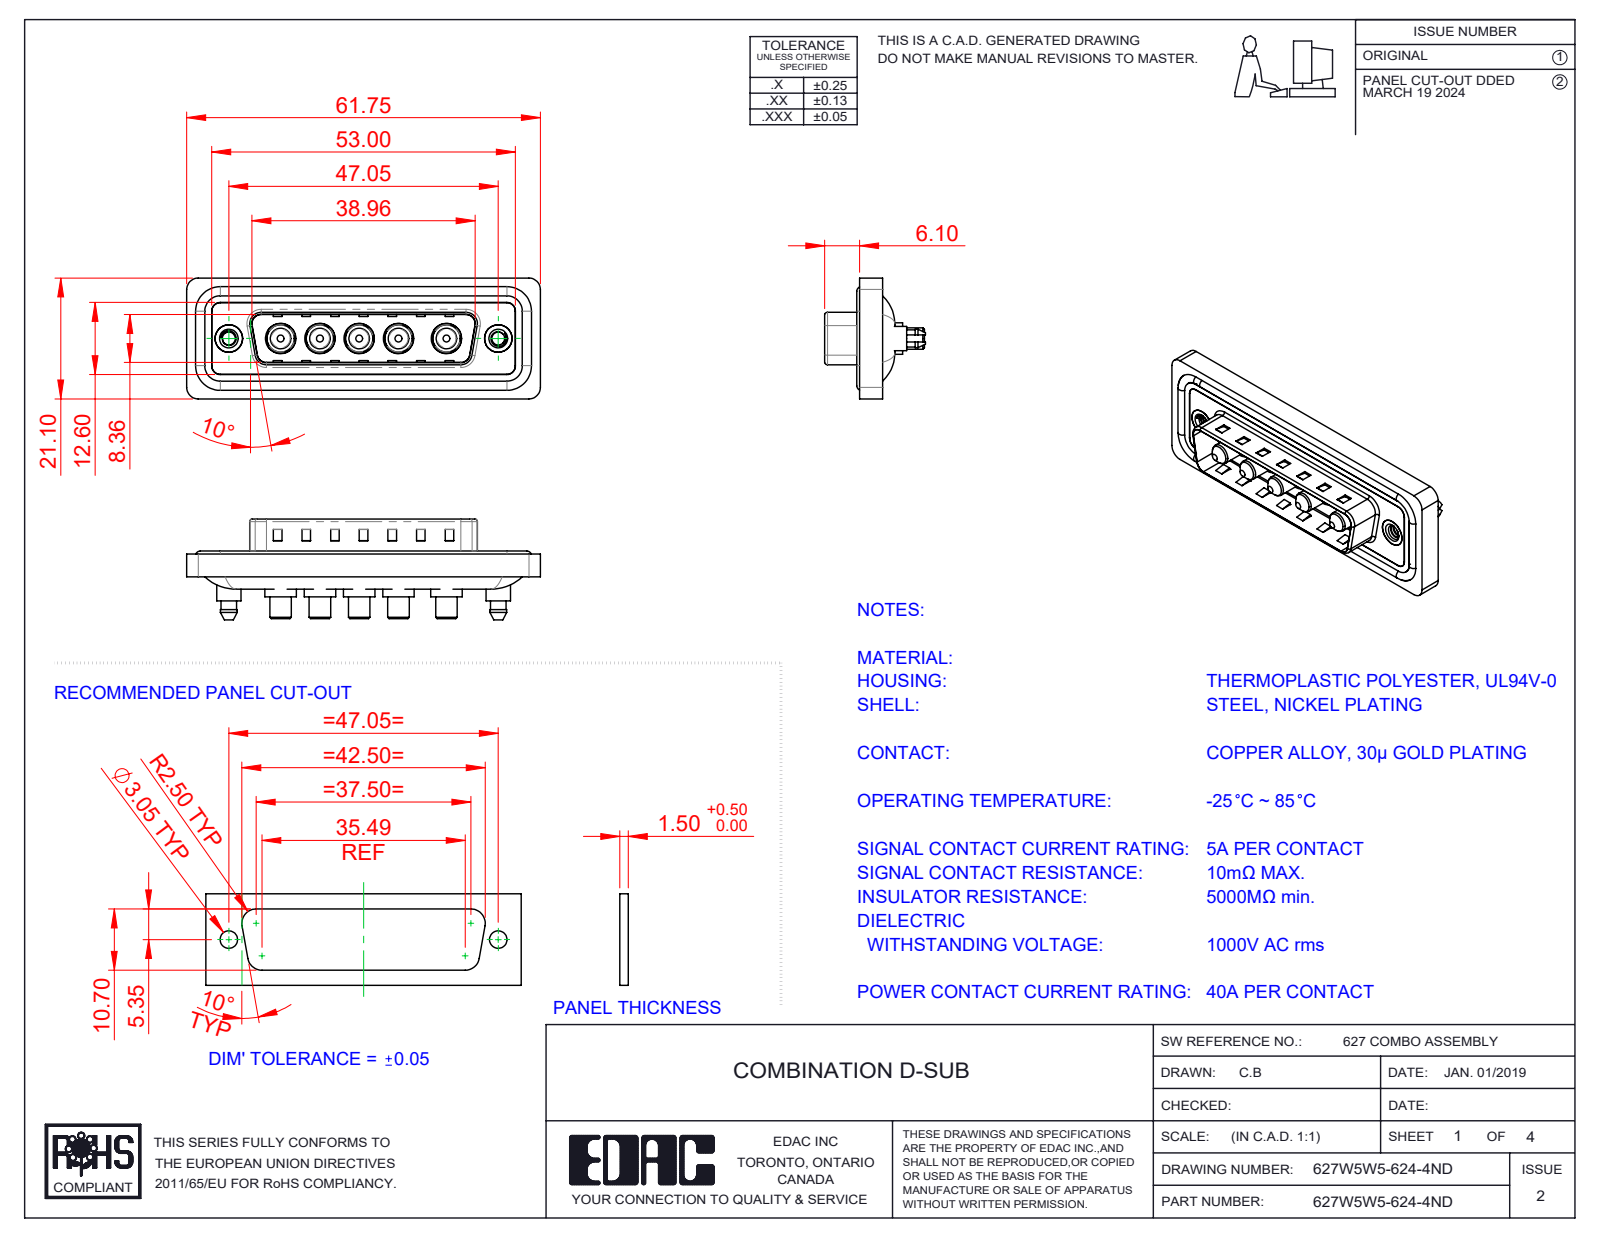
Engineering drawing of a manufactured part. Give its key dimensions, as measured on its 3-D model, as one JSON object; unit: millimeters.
{"part_name": "627Combo Housing_5W5; 627Combo Shell Front_25 Contacts; 627W5W5-624-4ND; 627Combo Threaded Boardlock_D (+4 more)", "step_written_by": "SolidWorks 2023 (CONFIG_CONTROL_DESIGN)", "units": "millimeters", "bodies": {"solids": 17, "faces": 736, "planar": 275, "cylindrical": 323, "other": 138}, "overall_size": [61.75, 21.1, 17.6], "volume_mm3": 7700, "surface_area_mm2": 12187, "round_holes": [[4.85, 5], [5.3, 5], [2.26, 2], [4, 2], [4.8, 2], [5, 2]], "round_bosses_or_shafts": [[5.5, 5], [5.2, 5], [4.75, 5], [3.75, 5], [3.6, 5], [1.6, 4], [5.4, 2], [4.9, 2]], "partial_cylinders_radius": [[1.5, 24], [2, 18], [1.6, 10], [0.5, 8], [2.1, 5], [0.25, 4], [0.6, 4], [0.65, 4]], "face_to_face_distances": [0.4, 1.5, 3.1, 1.1, 0.5, 1.6, 2.9, 0.82, 9.58, 5.65], "hole_center_spacings": [6.86, 9.04, 13.73, 38.01, 6.87, 8.37, 8.38, 9.05]}
